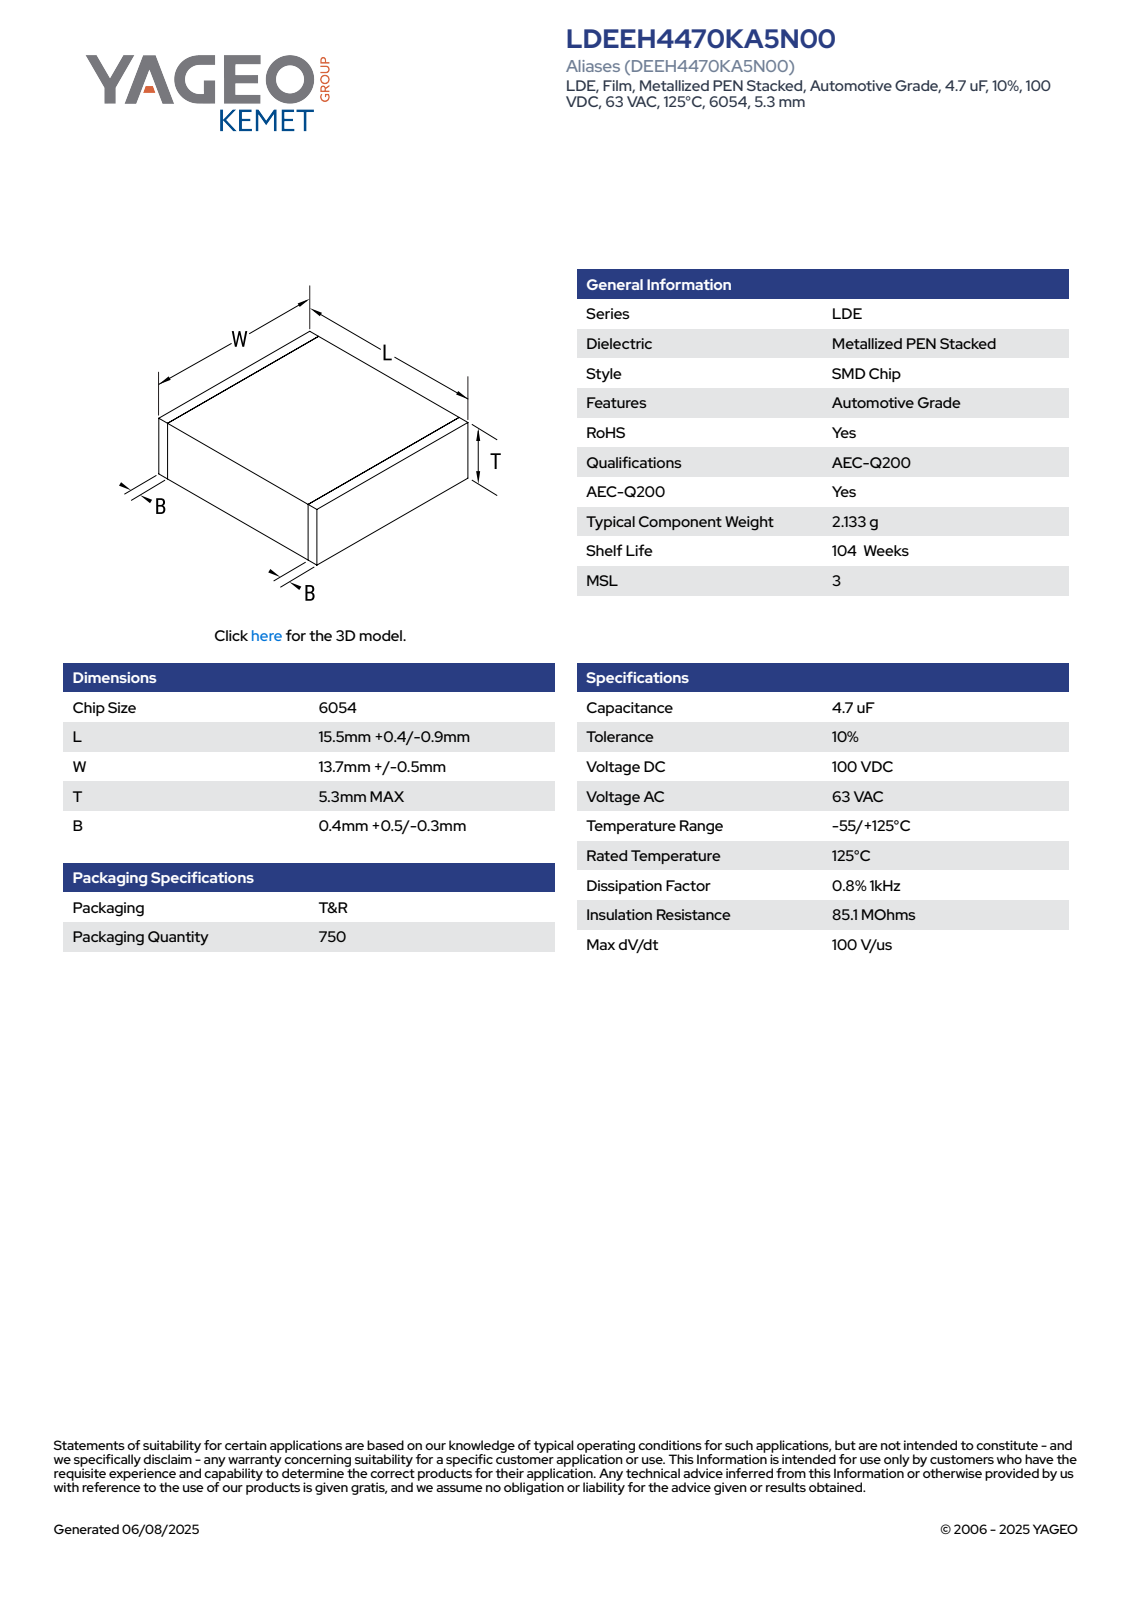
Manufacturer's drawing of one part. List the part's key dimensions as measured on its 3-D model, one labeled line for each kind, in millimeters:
Part name (STEP PRODUCT): CFS_LDELDB_6054_L15.9W14.2T5.3B0.9
STEP written by: SolidWorks 2020 (AUTOMOTIVE_DESIGN)
Units: millimetres
Bodies: 4 solids, 73 faces (73 planar, 0 cylindrical, 0 other)
Overall size (bounding box): 15.9 × 14.2 × 5.3
Volume: 1 191 mm³ · Surface area: 782 mm²
Main face-to-face distances: 5.28, 14.18, 15.9, 5.29, 5.3, 14.19, 14.2, 0.5, 15.4, 14.9
